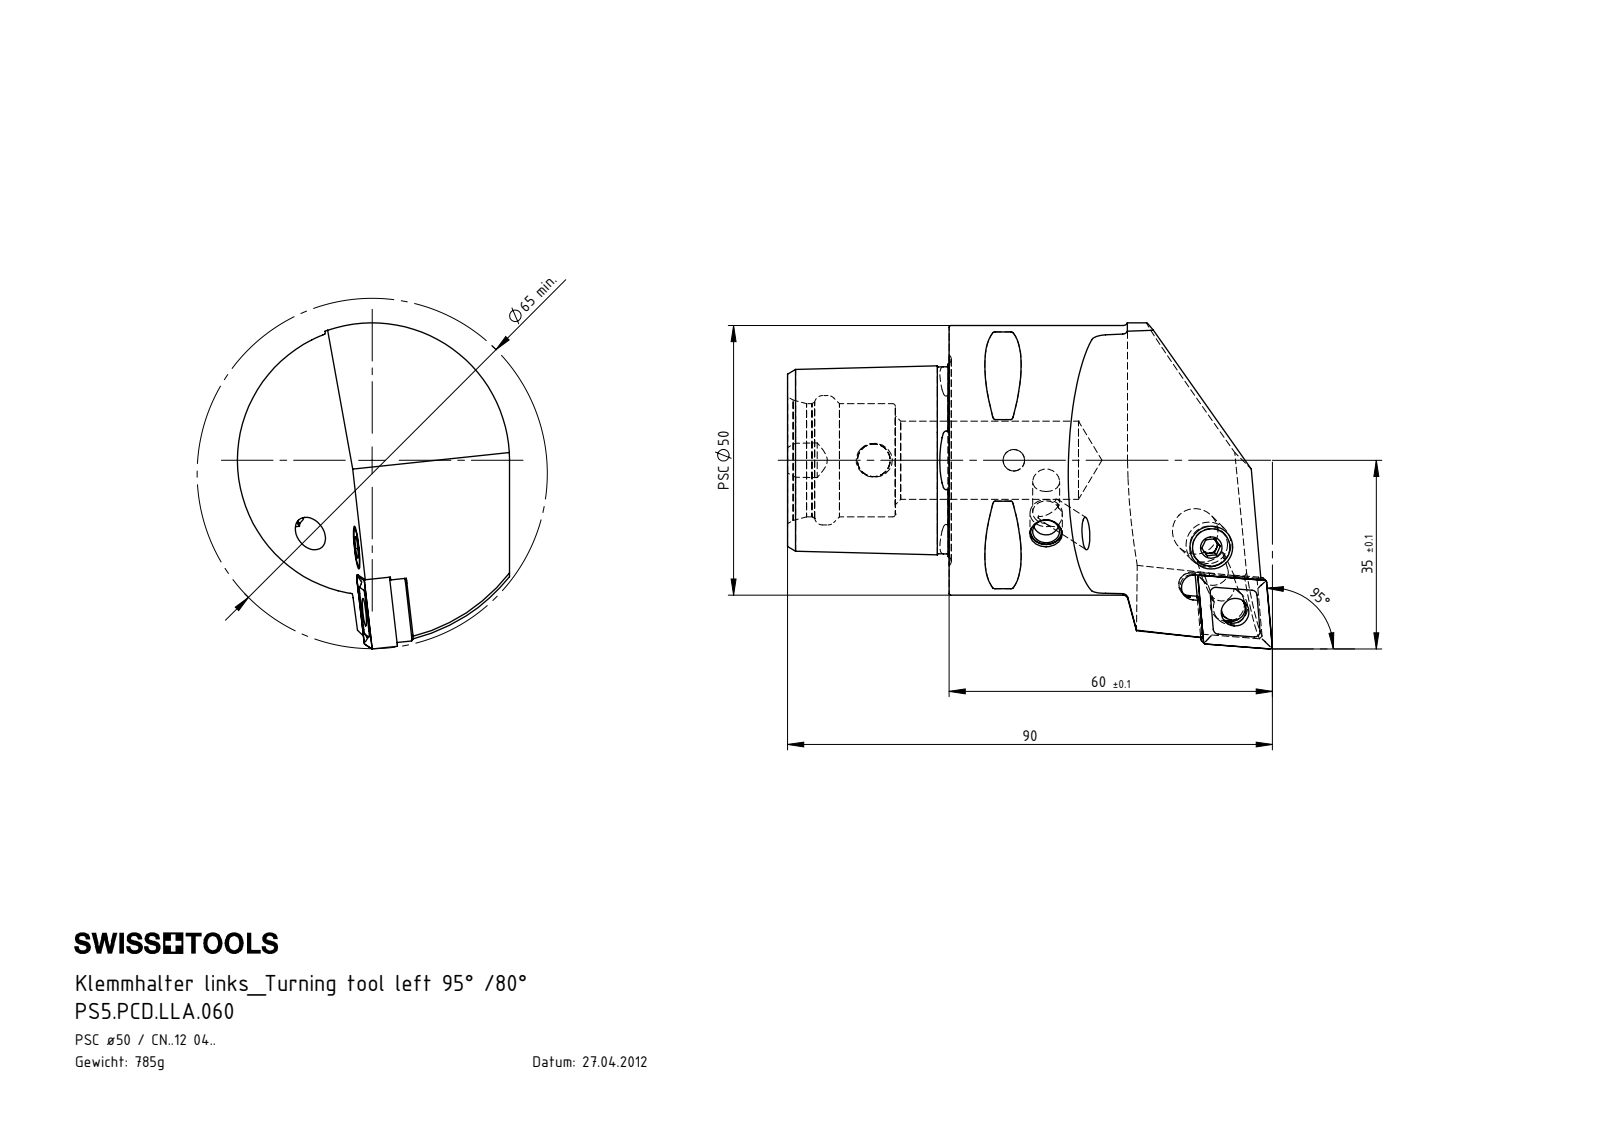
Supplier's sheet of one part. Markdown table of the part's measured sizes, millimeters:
| quantity | value |
| --- | --- |
| part name | PS5-PCD.LLA.060_A; PS5-PCD.LLA.060; WCD-ER4.101.017_A; WCD-ER3.101.000_A (+4 more) |
| STEP written by | SolidWorks 2012 (CONFIG_CONTROL_DESIGN) |
| units | millimeters |
| bodies | 8 solids, 342 faces (93 planar, 85 cylindrical, 164 other) |
| overall size | 90 × 60.5 × 50.5 |
| volume | 99 152 mm³ |
| surface area | 22 004 mm² |
| round holes (diameter × count) | 5 × 3, 4 × 1, 5.16 × 1, 6 × 1, 6.1 × 1, 6.4 × 1, 7 × 1, 8.4 × 1, 14.5 × 1, 21 × 1, 24 × 1 |
| round bosses / shafts (diameter × count) | 50 × 1, 8 × 1, 7.9 × 1, 6.4 × 1, 6 × 1, 4.5 × 1, 3.55 × 1 |
| partial cylindrical surfaces (radius × count) | 0.5 × 8, 0.4 × 4, 1 × 4, 2.5 × 2, 2.1 × 1, 2.2 × 1, 2.35 × 1, 2.8 × 1 |
| main face-to-face distances | 30, 19.18, 3.18, 4.47, 44.4, 20, 10, 0.5, 7.65, 3.19 |
| hole center spacings | 12.8, 12.86, 26 |
